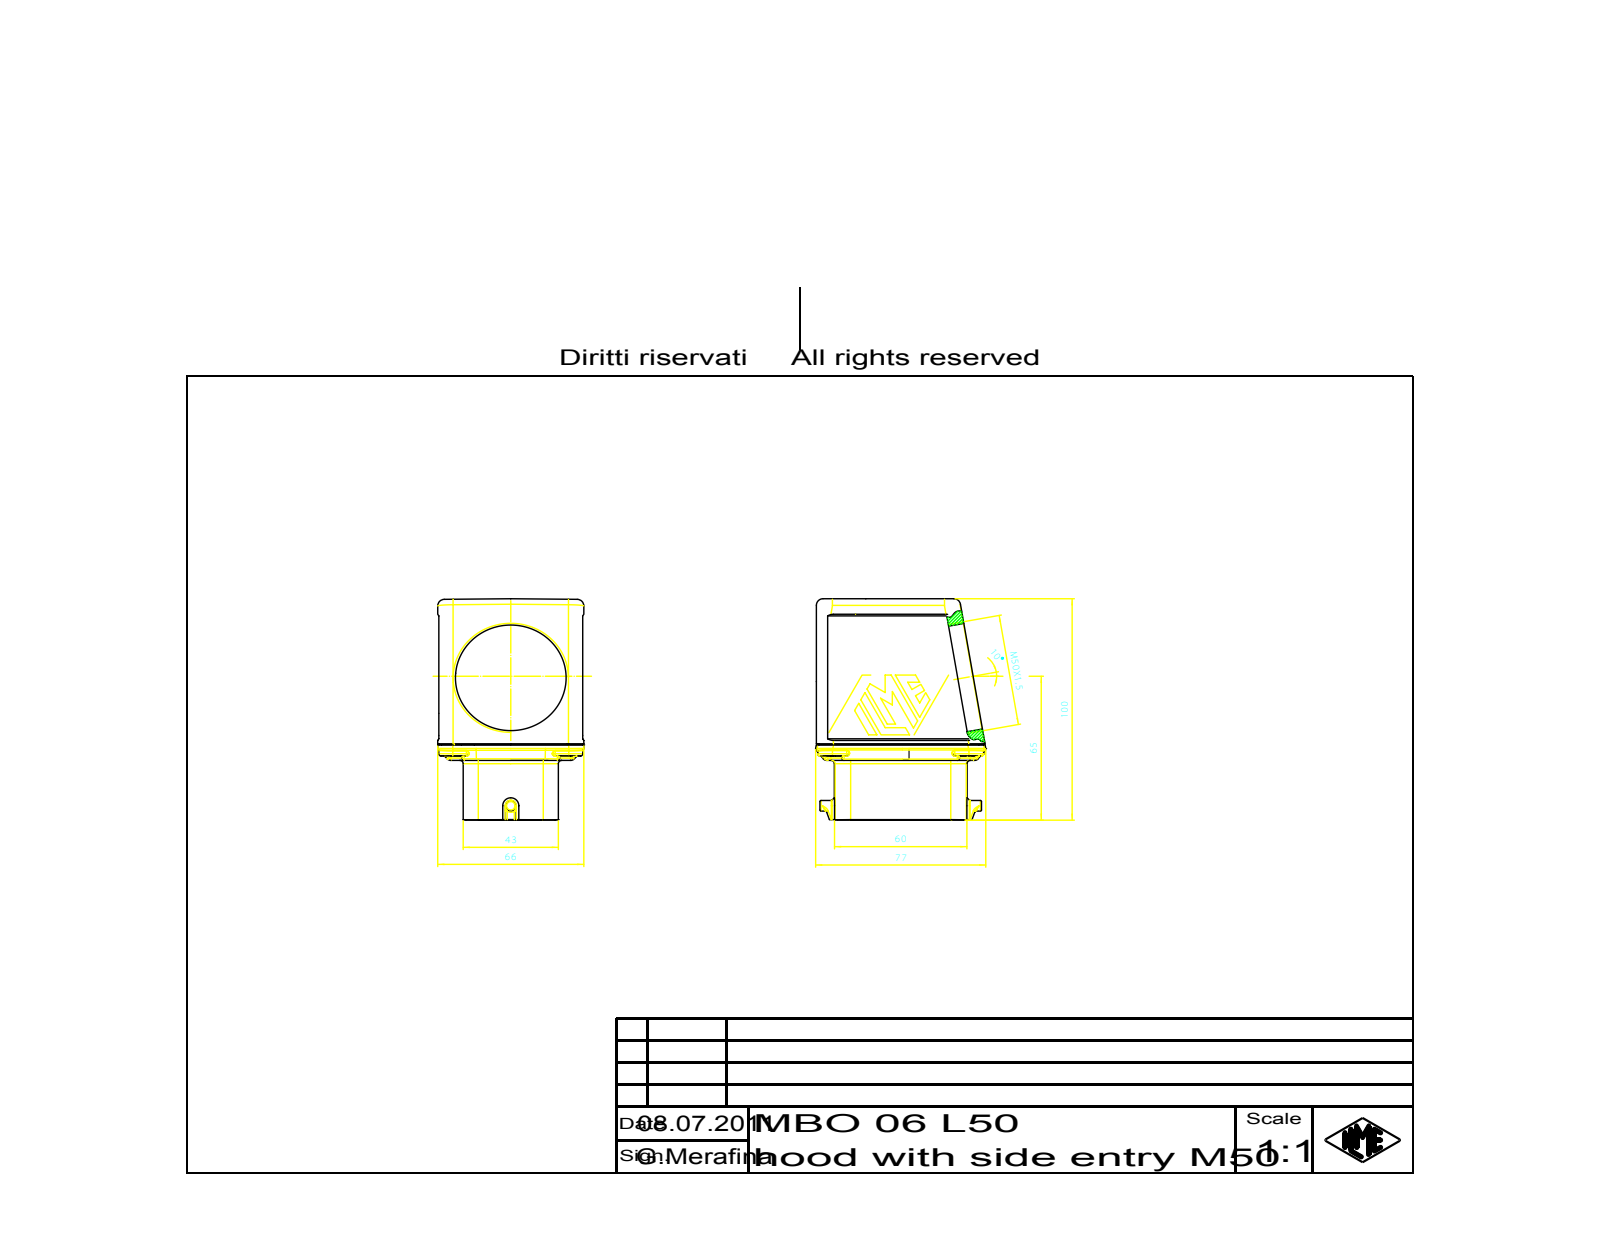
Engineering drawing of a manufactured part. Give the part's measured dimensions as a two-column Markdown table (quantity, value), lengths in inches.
| quantity | value |
| --- | --- |
| part name | 53848_Body_1_Body_1.1 |
| STEP written by | CoCreate Modeling 16.00A 16-Aug-2008 (C) Parametric Technology GmbH (AUTOMOTIVE_DESIGN) |
| units | inches |
| bodies | 1 solid, 561 faces (265 planar, 140 cylindrical, 156 other) |
| overall size | 3.917 × 2.983 × 2.599 |
| volume | 18.09 in³ |
| surface area | 65.9 in² |
| round holes (diameter × count) | 1.969 × 1 |
| round bosses / shafts (diameter × count) | 0.189 × 1 |
| partial cylindrical surfaces (radius × count) | 0.039 × 46, 0.012 × 18, 0.276 × 14, 0.118 × 10, 0.059 × 6, 0.02 × 4, 0.165 × 4, 0.197 × 4 |
| main face-to-face distances | 2.863, 2.559, 0.016, 2.575, 0.976, 0.433, 2.126, 2.126, 1.693, 0.433 |
